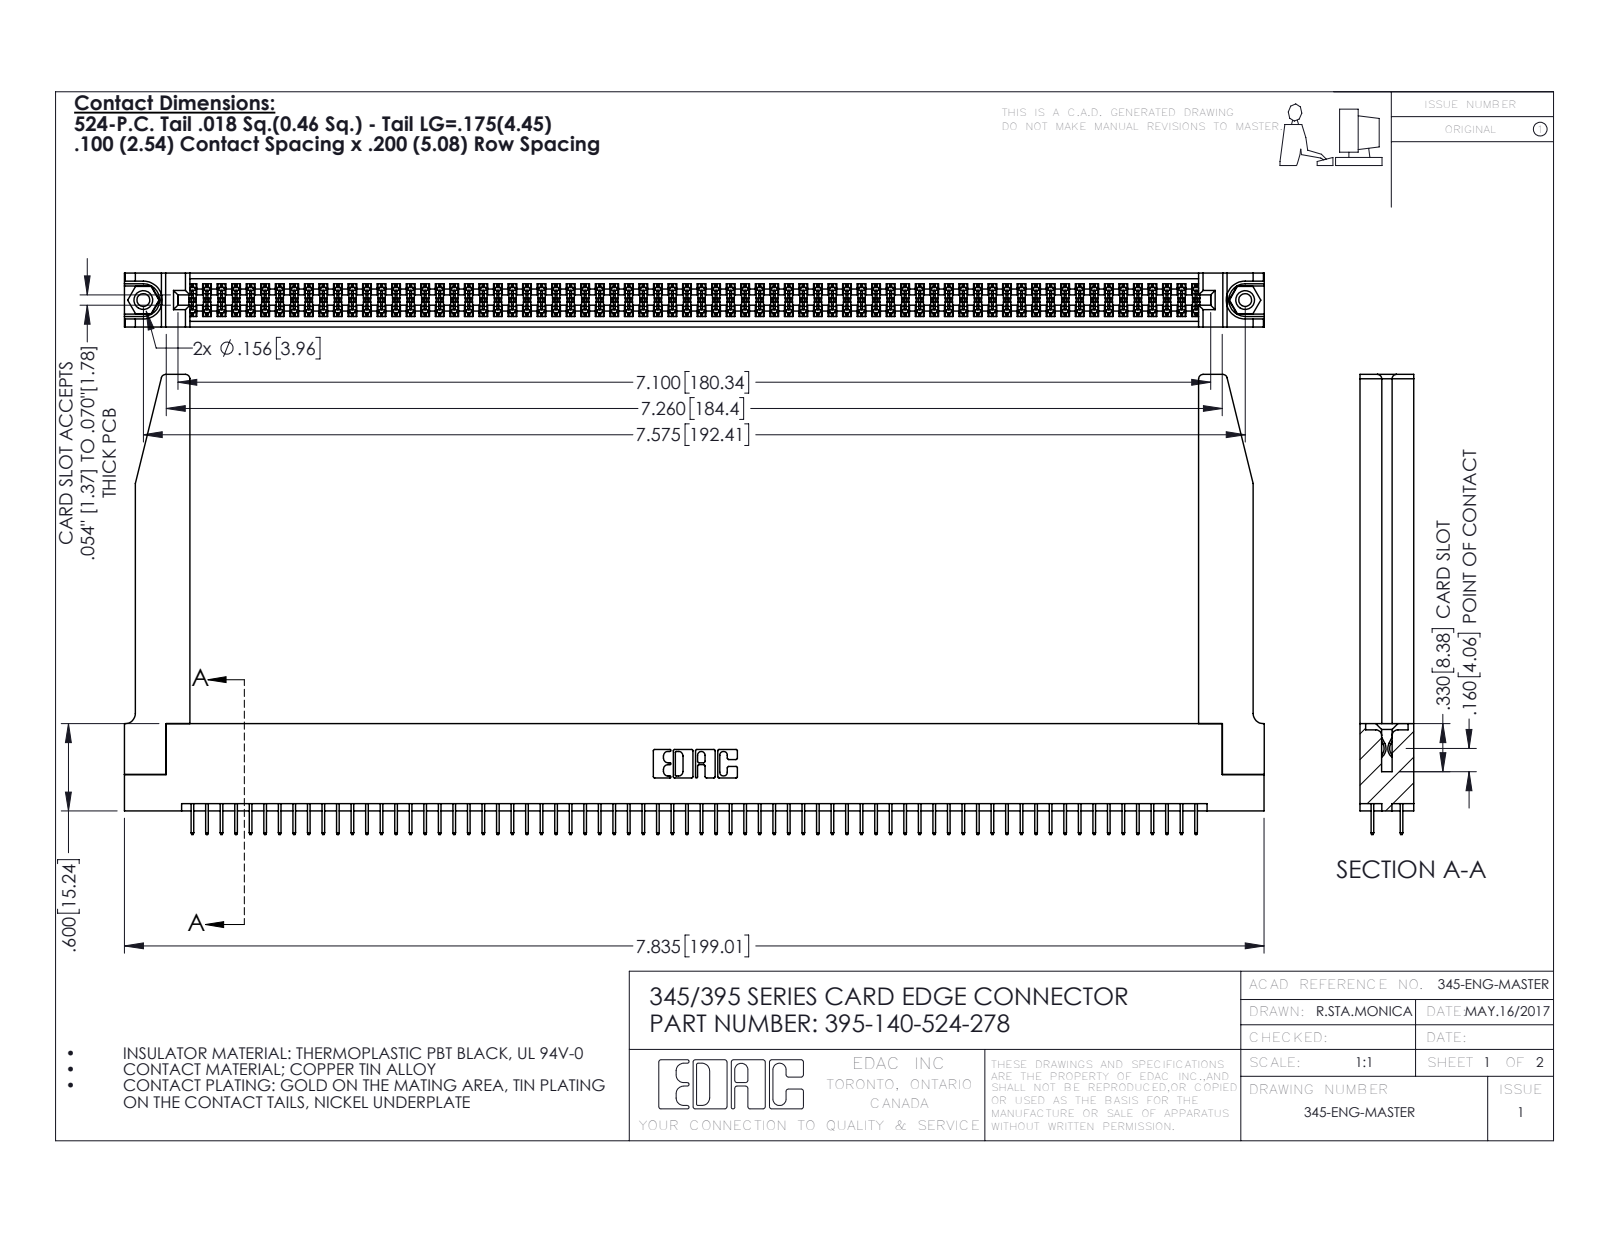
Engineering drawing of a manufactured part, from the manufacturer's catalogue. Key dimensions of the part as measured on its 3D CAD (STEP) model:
Part name (STEP PRODUCT): 395-140-524-278; 345-220-078_345-220-078; 345-292-001_345-293-124; 345-250-001_345-250-001-102 (+1 more)
STEP written by: SolidWorks 2016 (CONFIG_CONTROL_DESIGN)
Units: inches
Bodies: 145 solids, 7920 faces (5682 planar, 2186 cylindrical, 52 other)
Overall size (bounding box): 7.836 × 3.162 × 0.37
Volume: 1.657 in³ · Surface area: 54.98 in²
Round holes (diameter × count): ⌀0.089 ×2, ⌀0.125 ×2, ⌀0.156 ×2, ⌀0.064 ×1
Round bosses / shafts (diameter × count): ⌀0.155 ×2
Partial cylindrical surfaces — rounded edges, fillets, slot ends (radius × count): R0.006 ×210, R0.01 ×22, R0.03 ×8, R0.007 ×6, R0.031 ×6, R0.026 ×3, R0.014 ×2, R0.019 ×2
Main face-to-face distances: 0.072, 0.298, 0.37, 0.2, 0.098, 0.272, 0.025, 0.225, 0.072, 0.175
Hole centre spacings: 0.27, 7.339, 7.575
